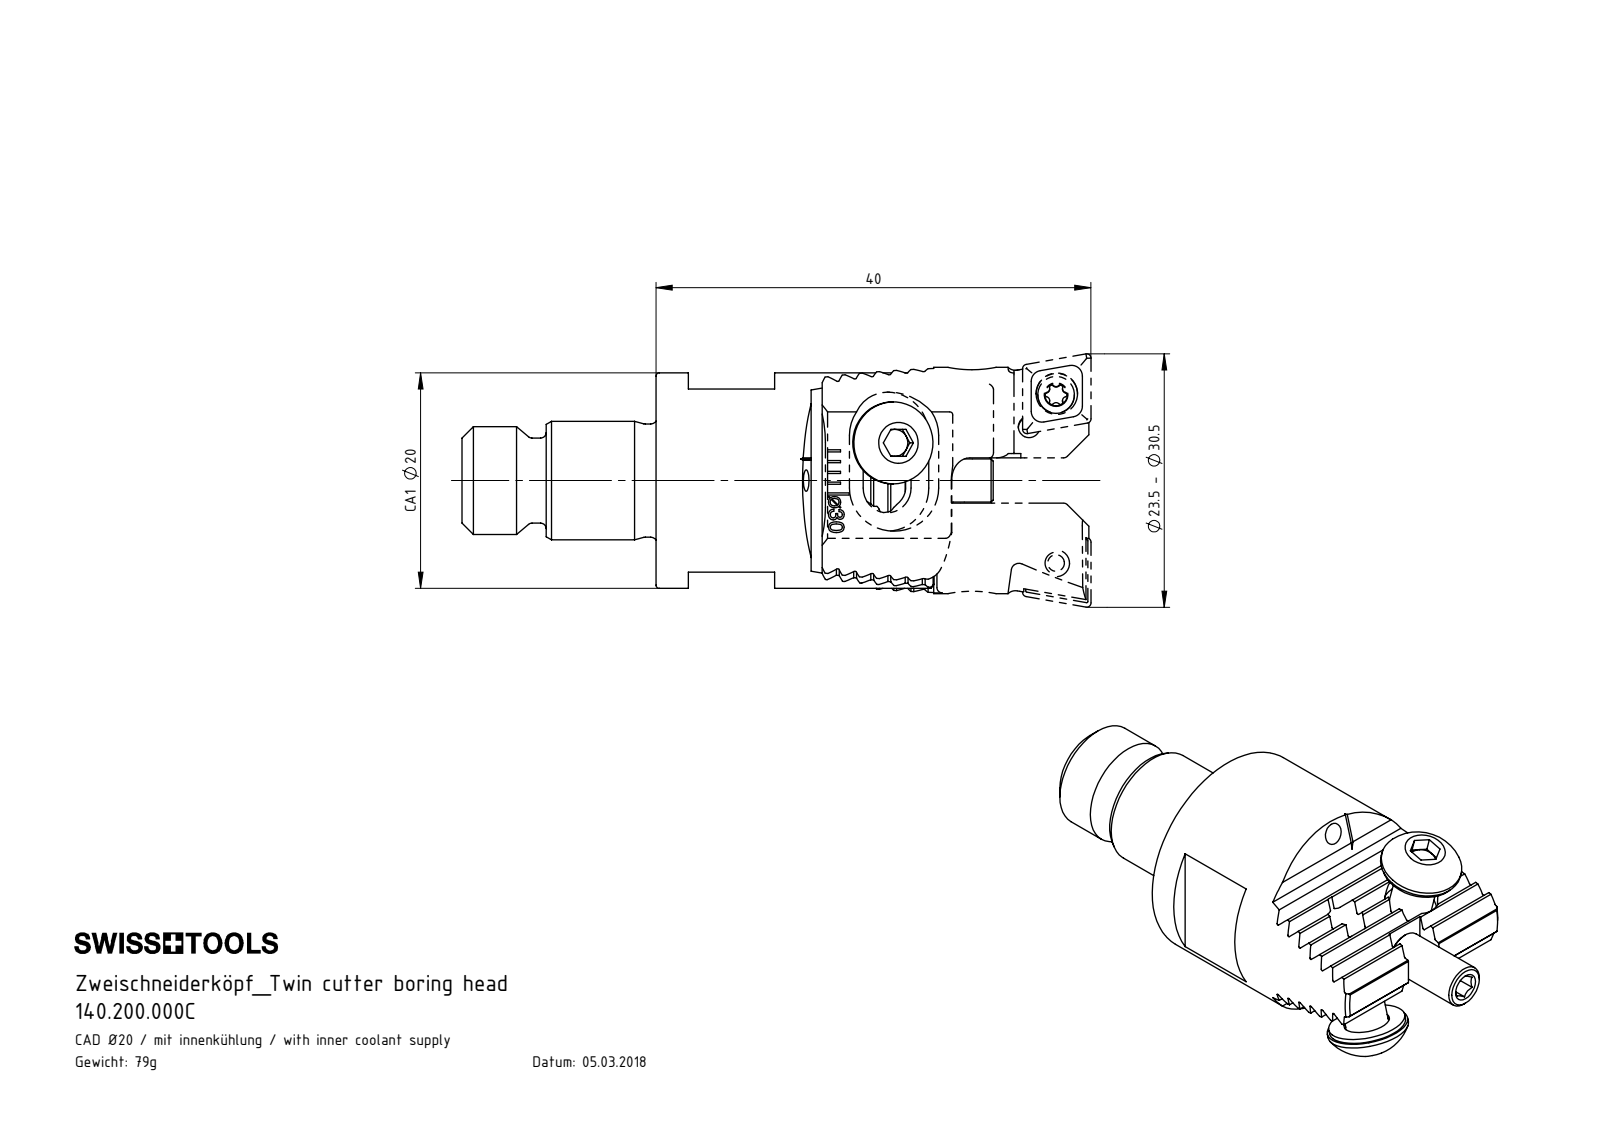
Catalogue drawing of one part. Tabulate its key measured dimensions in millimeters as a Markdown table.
| quantity | value |
| --- | --- |
| part name | Z20-ER2.001.013_A; Z20-ER1.001.008; CA1-Z20.K23.040_A; Z20-ER1.003.008_A_gespannt (+2 more) |
| STEP written by | SolidWorks 2017 (CONFIG_CONTROL_DESIGN) |
| units | millimeters |
| bodies | 6 solids, 325 faces (158 planar, 95 cylindrical, 72 other) |
| overall size | 49.3 × 20 × 20 |
| volume | 7 349 mm³ |
| surface area | 4 157 mm² |
| round holes (diameter × count) | 2 × 4, 3.3 × 2, 4.3 × 2, 5 × 2, 2.5 × 1 |
| round bosses / shafts (diameter × count) | 4 × 3, 7.6 × 2, 7.2 × 2, 20 × 1, 11 × 1, 10.5 × 1, 10 × 1, 7.9 × 1 |
| partial cylindrical surfaces (radius × count) | 0.12 × 14, 220 × 2 |
| main face-to-face distances | 1.43, 2.86, 4.29, 5.72, 7.15, 3.8, 17, 3.4, 11.4, 0.4 |
